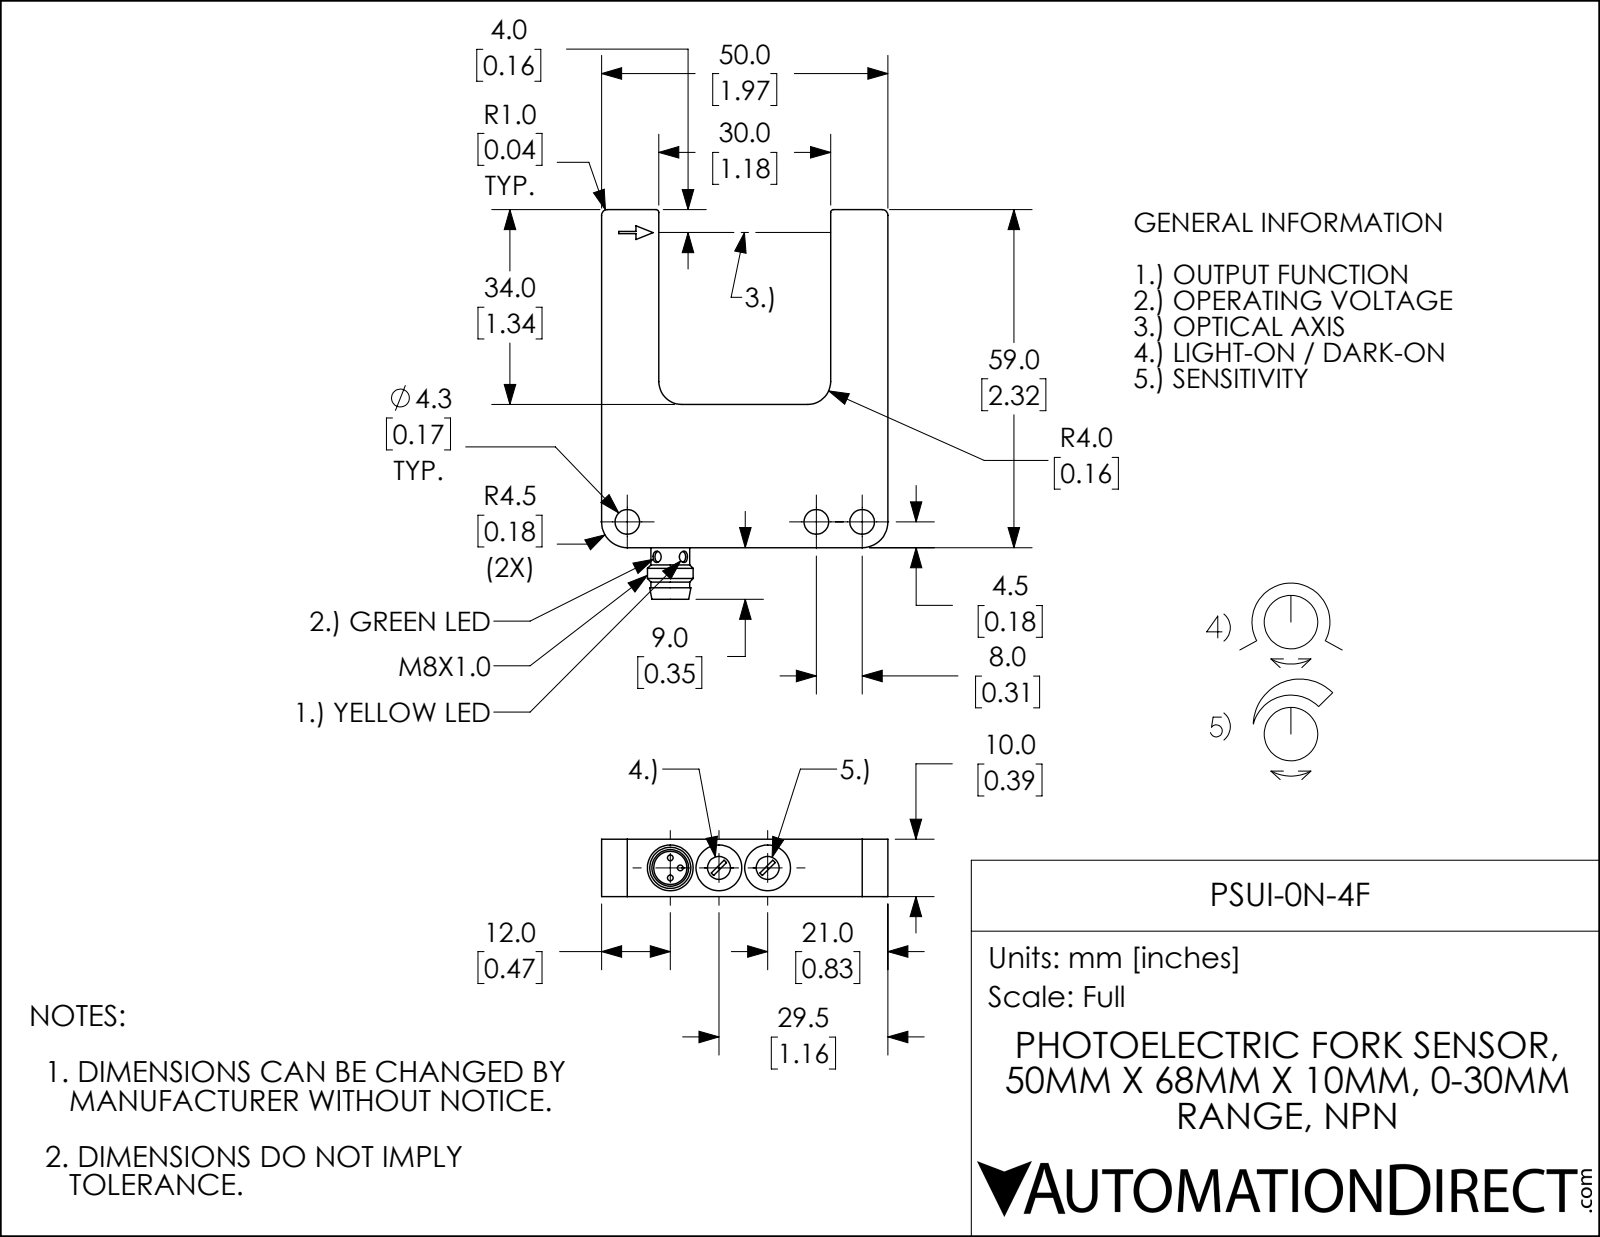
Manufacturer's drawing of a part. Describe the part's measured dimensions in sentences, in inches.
The part is named "PSUI-0N-4F". Its 3-D file was written by "SolidWorks 2017 (AUTOMOTIVE_DESIGN)". It is 1 solid with 71 faces: 35 planar, 30 cylindrical and 6 other. Overall it measures 2.677 by 1.969 by 0.394 inches. Its volume is 1.163 cubic inches and its surface area 11.35 square inches. Round holes: 3 of diameter 0.169, 2 of diameter 0.079, 2 of diameter 0.157, 2 of diameter 0.315, 1 of diameter 0.228. Round bosses or shafts: 3 of diameter 0.039, 1 of diameter 0.315, 1 of diameter 0.267. Partial cylindrical surfaces (rounded edges, fillets, slot ends): 2 of radius 0.02, 2 of radius 0.039, 2 of radius 0.063, 2 of radius 0.157, 2 of radius 0.177. The main face-to-face distances are 0.394, 1.575, 1.969, 1.181, 0.984, 1.339, 2.323, 2.319, 0.98, 0.157. The hole center spacings are 0.335, 0.315, 0.669, 1.299, 1.614.
